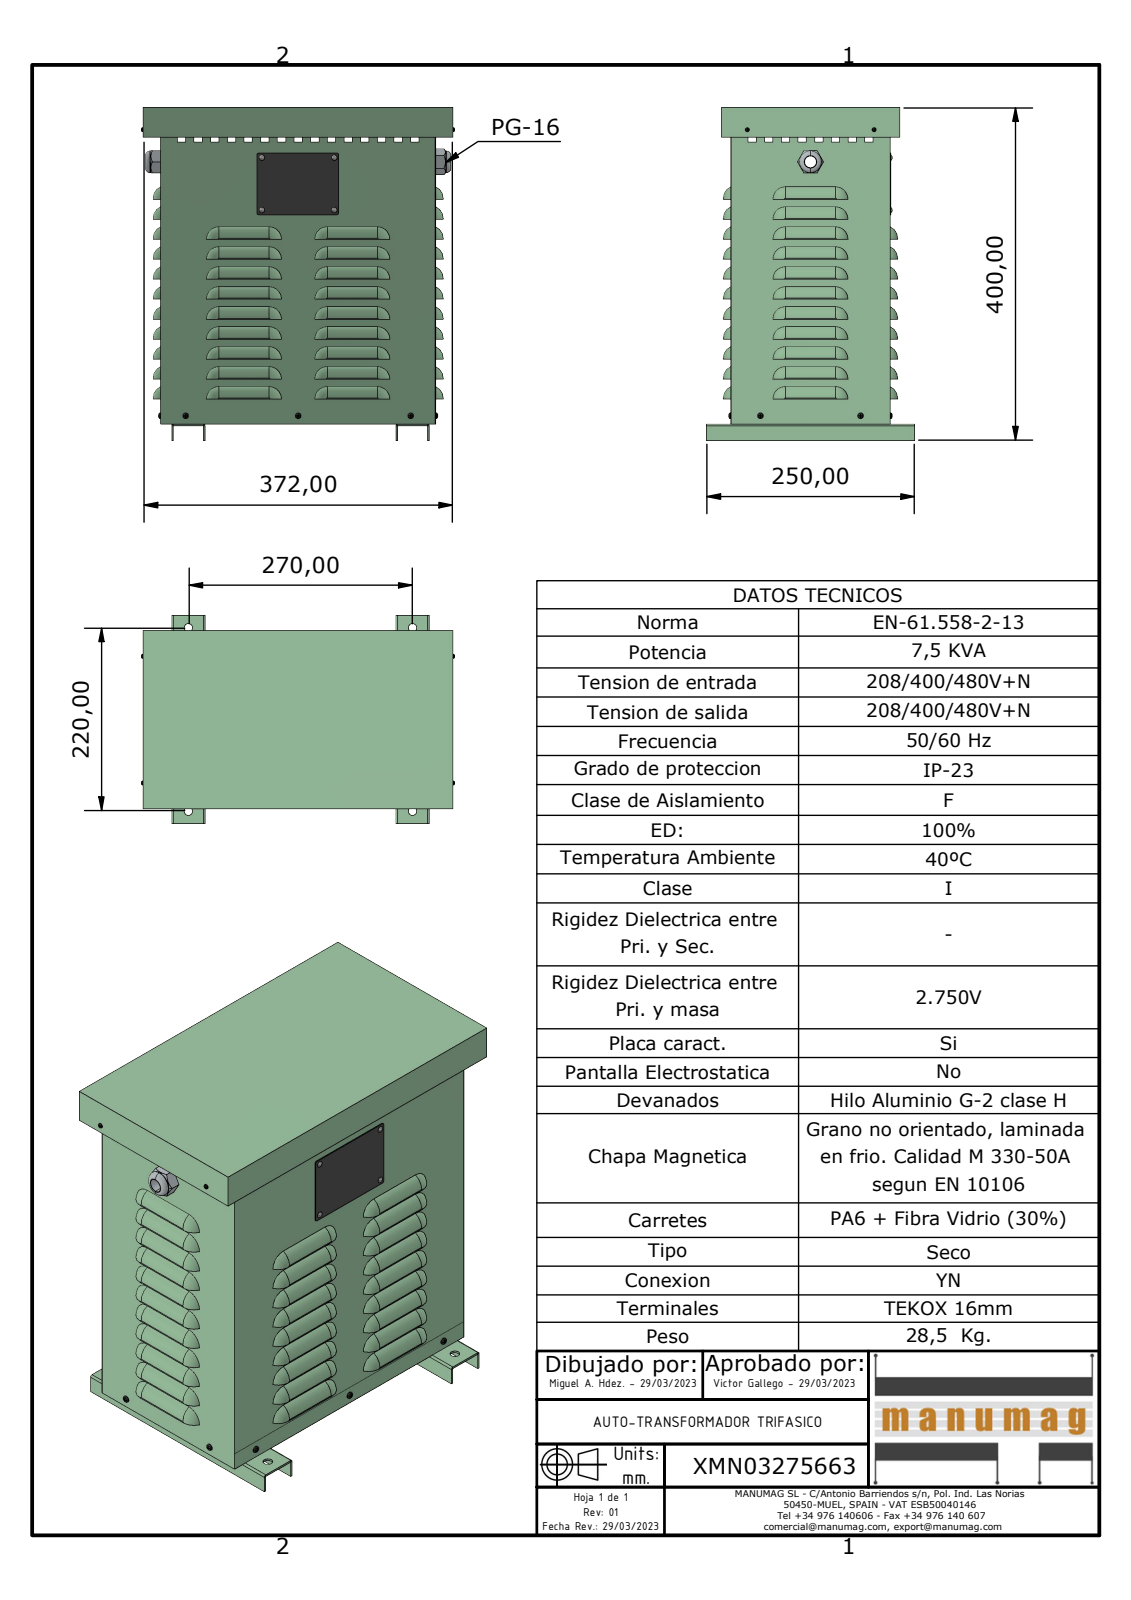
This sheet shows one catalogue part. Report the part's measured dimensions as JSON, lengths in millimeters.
{"part_name": "XMN03275663; JE010 NACIONAL CUERPO; JE010 NACIONAL BASE; PLACA CARACTERISTICAS (+6 more)", "step_written_by": "Autodesk Inventor 2023 (AUTOMOTIVE_DESIGN)", "units": "millimeters", "bodies": {"solids": 26, "faces": 1888, "planar": 958, "cylindrical": 396, "other": 534}, "overall_size": [400.63, 376.16, 250], "volume_mm3": 883061, "surface_area_mm2": 1346000, "round_holes": [[4, 9], [3, 4], [10, 4], [14, 1], [24, 1]], "round_bosses_or_shafts": [[3.5, 5], [3.18, 5], [3.2, 4], [2.5, 2], [2.26, 2], [26, 1], [23, 1], [22.5, 1]], "partial_cylinders_radius": [[14, 66], [7, 42], [15, 42], [1.5, 12], [5, 8], [5.5, 8], [0.5, 5], [0.5, 4]], "face_to_face_distances": [0.5, 190.5, 1.5, 190, 379.12, 329.5, 191, 380.62, 329, 330], "hole_center_spacings": [63, 85.25, 87, 107.42, 135, 152, 220, 250.8]}
